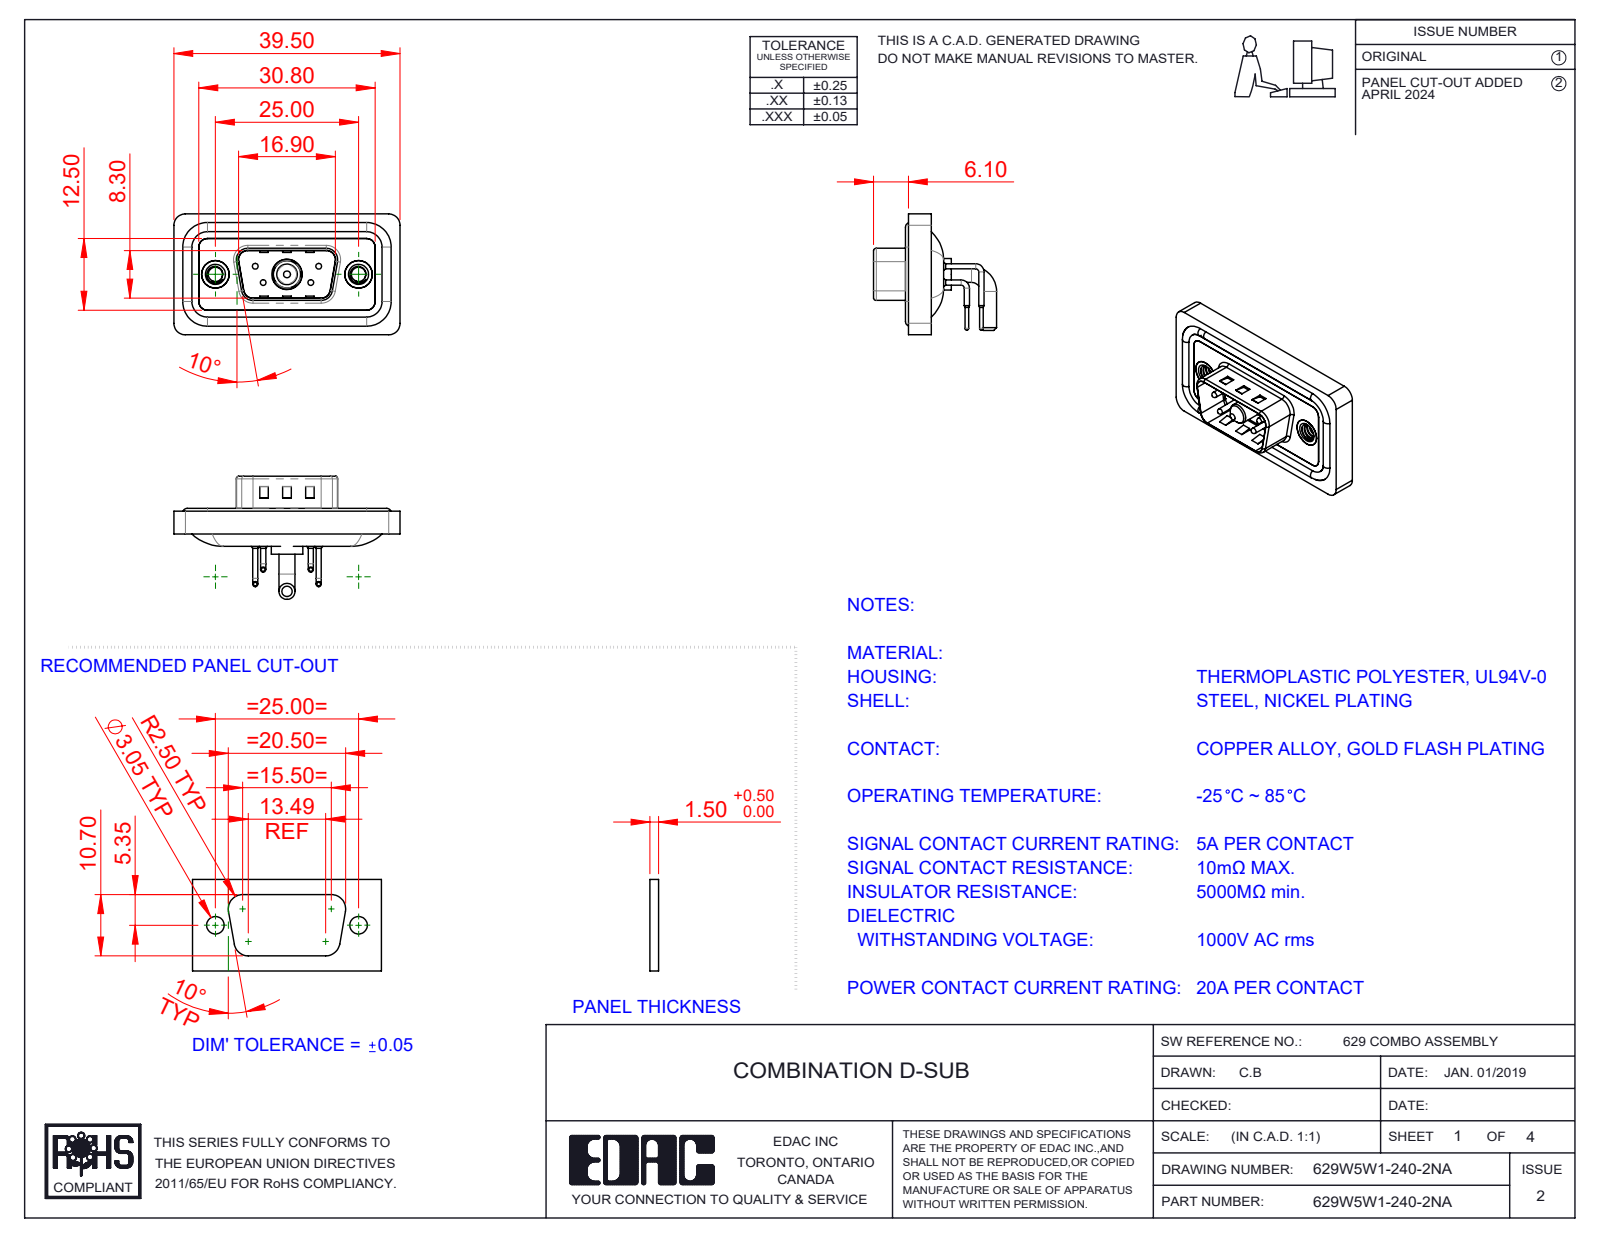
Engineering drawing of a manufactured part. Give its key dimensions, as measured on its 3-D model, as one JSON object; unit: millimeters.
{"part_name": "629Combo Shell Front_09 Contacts; 629Combo Contact Row 2; Power Pin_20A RA; 629W5W1-240-2NA (+5 more)", "step_written_by": "SolidWorks 2023 (CONFIG_CONTROL_DESIGN)", "units": "millimeters", "bodies": {"solids": 13, "faces": 888, "planar": 411, "cylindrical": 343, "other": 134}, "overall_size": [39.5, 21.5, 21.1], "volume_mm3": 4479, "surface_area_mm2": 7167, "round_holes": [[0.75, 4], [1.6, 4], [2, 4], [2.5, 2], [4, 2], [4.8, 2], [5, 2], [4.85, 1], [5.3, 1]], "round_bosses_or_shafts": [[0.9, 8], [1.6, 4], [1.5, 4], [1, 4], [0.65, 4], [4.9, 2], [2.8, 2], [5.5, 1]], "partial_cylinders_radius": [[1.5, 18], [2, 18], [0.5, 8], [1.6, 8], [0.25, 4], [0.6, 4], [0.65, 4], [0.9, 4]], "face_to_face_distances": [0.4, 2.9, 1.1, 0.8, 2.1, 2.5, 1.6, 3.1, 4.5, 1.5], "hole_center_spacings": [3.16, 5.72, 7.1, 12.5, 18.1, 4.39, 4.4, 8.31]}
